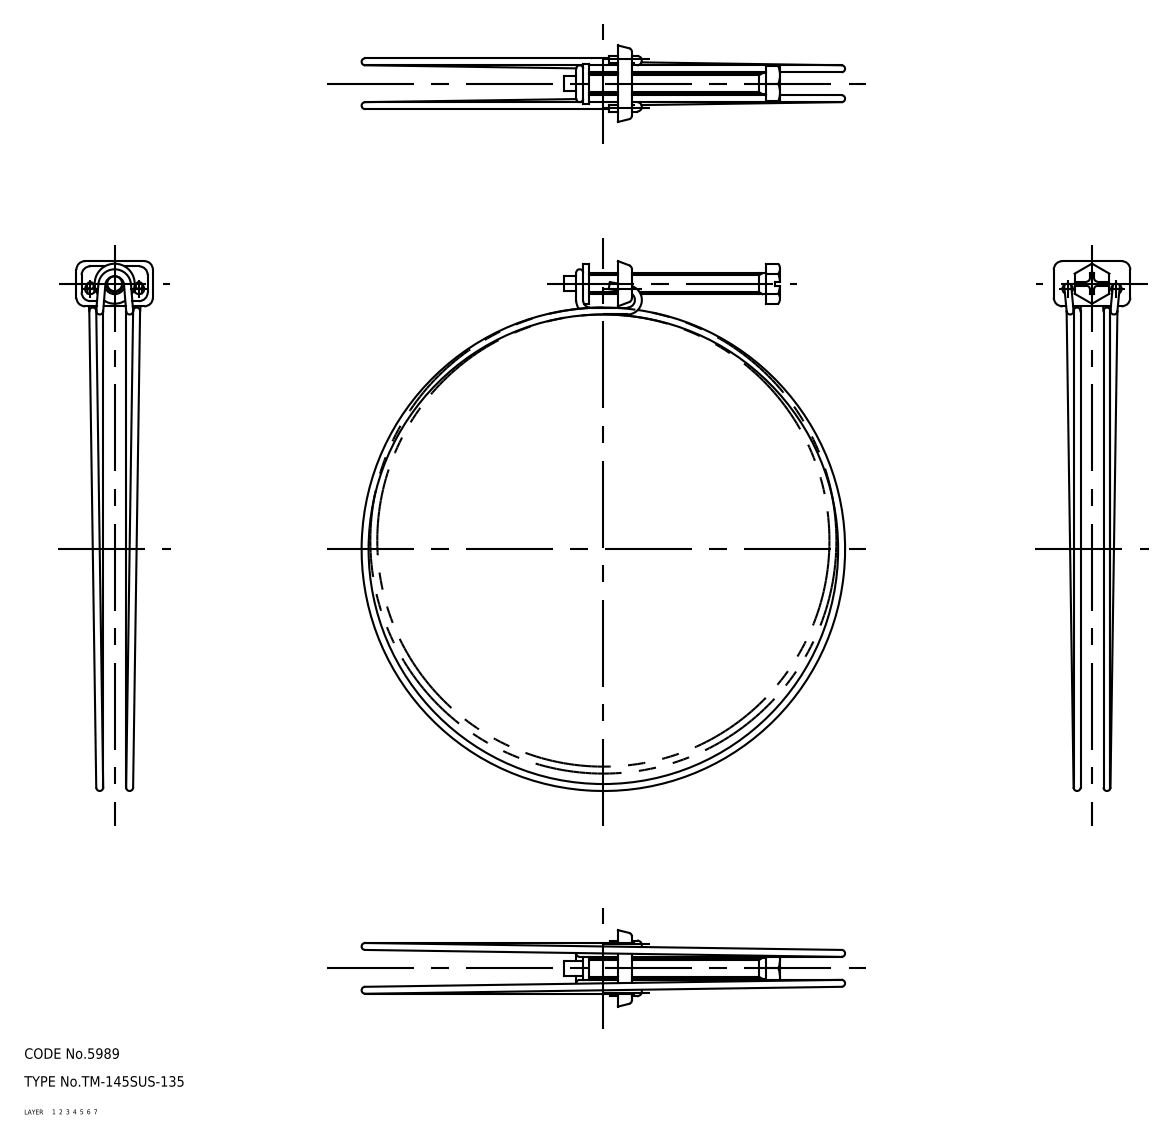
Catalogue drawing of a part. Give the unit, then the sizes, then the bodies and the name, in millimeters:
Units: millimetres
Overall size (bounding box): 152.35 × 139 × 22
Volume: 5 459 mm³ · Surface area: 8 326 mm²
Bodies: 3 solids, 119 faces (0 planar, 0 cylindrical, 119 other)
Part name (STEP PRODUCT): screw; holder; band; TM_145SUS_135_21491_36
STEP written by: CADfix (AUTOMOTIVE_DESIGN)
